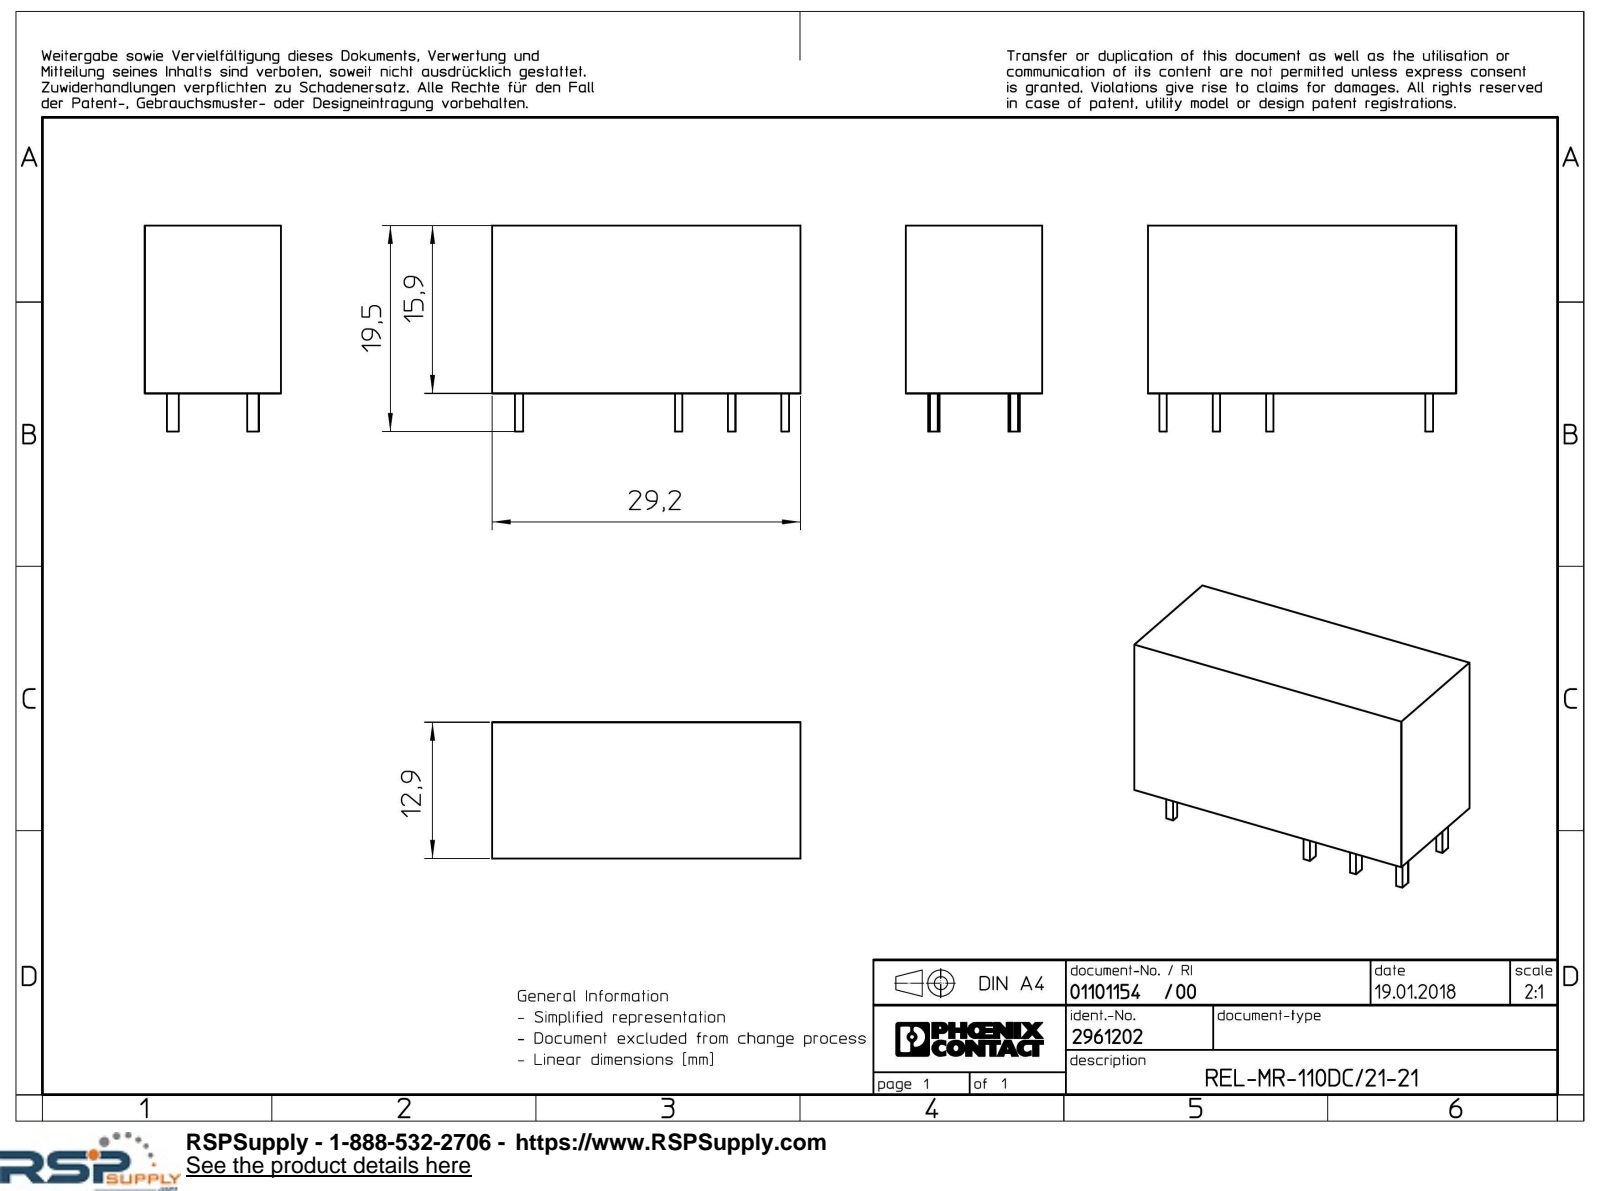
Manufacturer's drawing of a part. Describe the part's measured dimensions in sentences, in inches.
The part is named "REL-MR-29x16x13-select". Its 3-D file was written by "Creo Elements/Direct Modeling 18.1I 14-Aug-2016 (C) Parametric Technology GmbH (AUTOMOTIVE_DESIGN)". It is 1 solid with 46 faces: 46 planar, 0 cylindrical and 0 other. Overall it measures 1.15 by 0.768 by 0.508 inches. Its volume is 0.367 cubic inches and its surface area 3.398 square inches. The main face-to-face distances are 0.508, 0.626, 1.15, 0.199, 0.028, 0.425, 0.043, 0.299, 0.226, 0.398.
